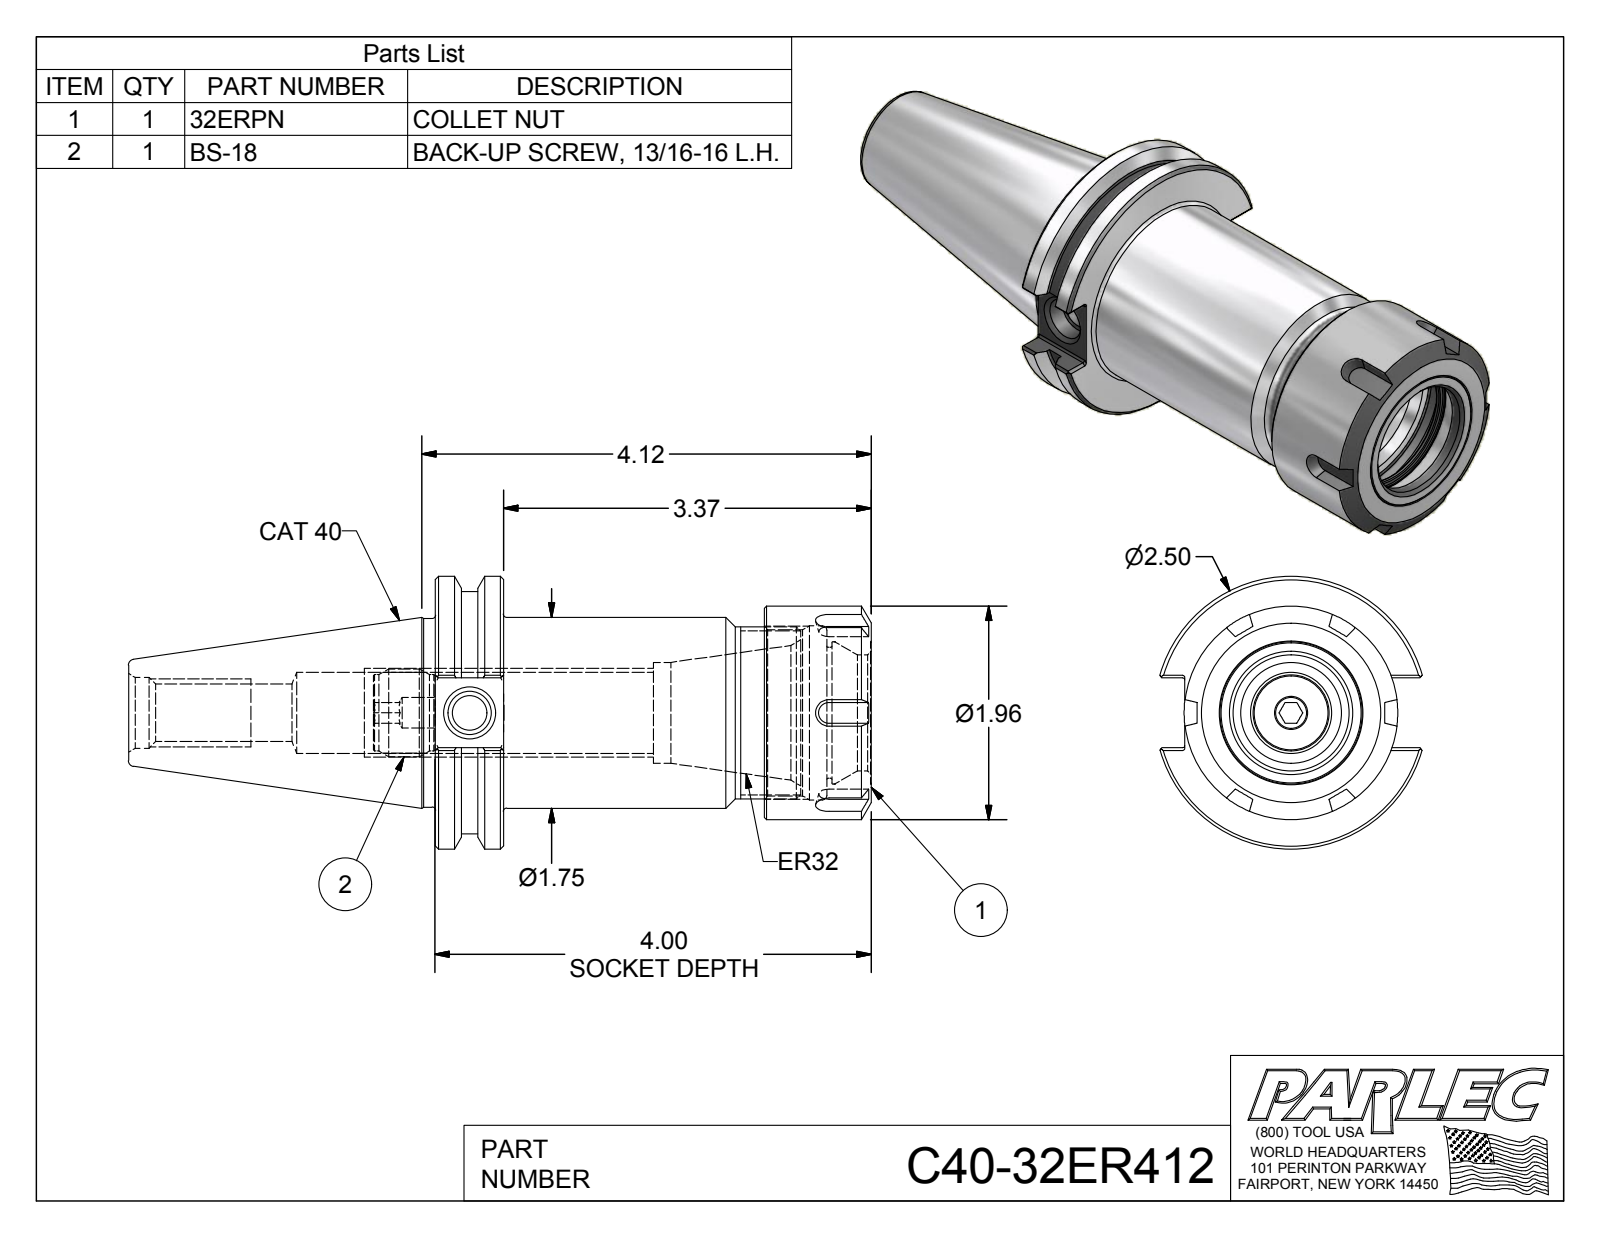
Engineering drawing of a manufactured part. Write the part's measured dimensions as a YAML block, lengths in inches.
part_name: "C40-32ER412; C40-32ER4-1; 32ERPN; BS-18"
step_written_by: "Autodesk Inventor 2012 (AUTOMOTIVE_DESIGN)"
units: inches
bodies: {solids: 3, faces: 148, planar: 63, cylindrical: 37, other: 48}
overall_size: [6.808, 2.5, 2.403]
volume: 11.69
surface_area: 70.88
round_holes:
  - {diameter: 0.28, count: 1}
  - {diameter: 0.315, count: 1}
  - {diameter: 0.399, count: 1}
  - {diameter: 0.527, count: 1}
  - {diameter: 0.648, count: 1}
  - {diameter: 0.745, count: 1}
  - {diameter: 0.925, count: 1}
  - {diameter: 1.063, count: 1}
  - {diameter: 1.2, count: 1}
  - {diameter: 1.305, count: 1}
  - {diameter: 1.523, count: 1}
  - {diameter: 1.595, count: 1}
round_bosses_or_shafts:
  - {diameter: 2.5, count: 1}
  - {diameter: 2.219, count: 1}
  - {diameter: 1.958, count: 1}
  - {diameter: 1.75, count: 1}
  - {diameter: 1.73, count: 1}
  - {diameter: 1.575, count: 1}
  - {diameter: 0.805, count: 1}
  - {diameter: 0.7, count: 1}
partial_cylinders:
  - {radius: 0.02, count: 12}
face_to_face_distances: [0.625, 3.995, 3.37, 3.017, 2.392, 0.978, 3.588, 2.963, 0.571, 0.407]
